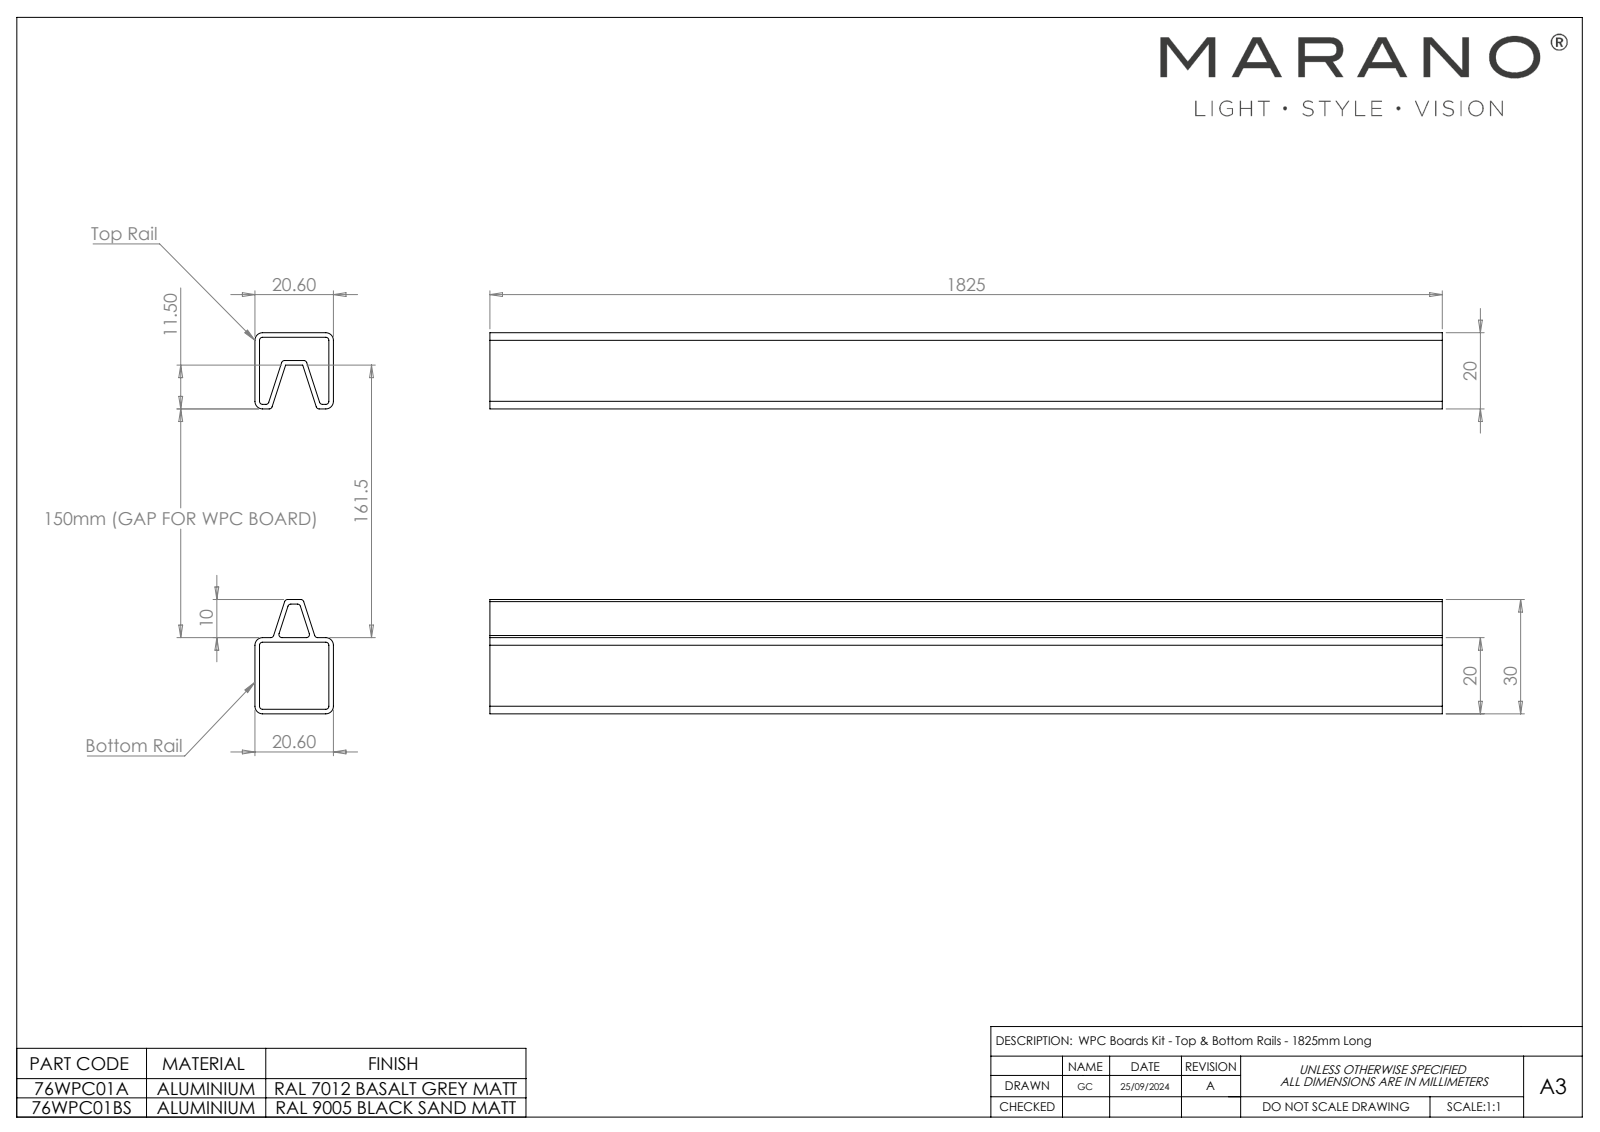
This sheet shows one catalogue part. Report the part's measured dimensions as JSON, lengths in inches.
{"part_name": "76FPBR18BS_1825mm; 76WPC01BS; 76FPTR18BS_1825mm", "step_written_by": "SolidWorks 2023 (CONFIG_CONTROL_DESIGN)", "units": "inches", "bodies": {"solids": 2, "faces": 67, "planar": 36, "cylindrical": 31, "other": 0}, "overall_size": [71.85, 3.937, 0.811], "volume_in3": 25.22, "surface_area_in2": 1049, "partial_cylinders_radius": [[0.031, 22], [0.079, 8]], "face_to_face_distances": [0.047, 0.764, 0.793, 3.89, 3.15, 0.74, 0.811, 0.717, 0.745, 3.197]}
